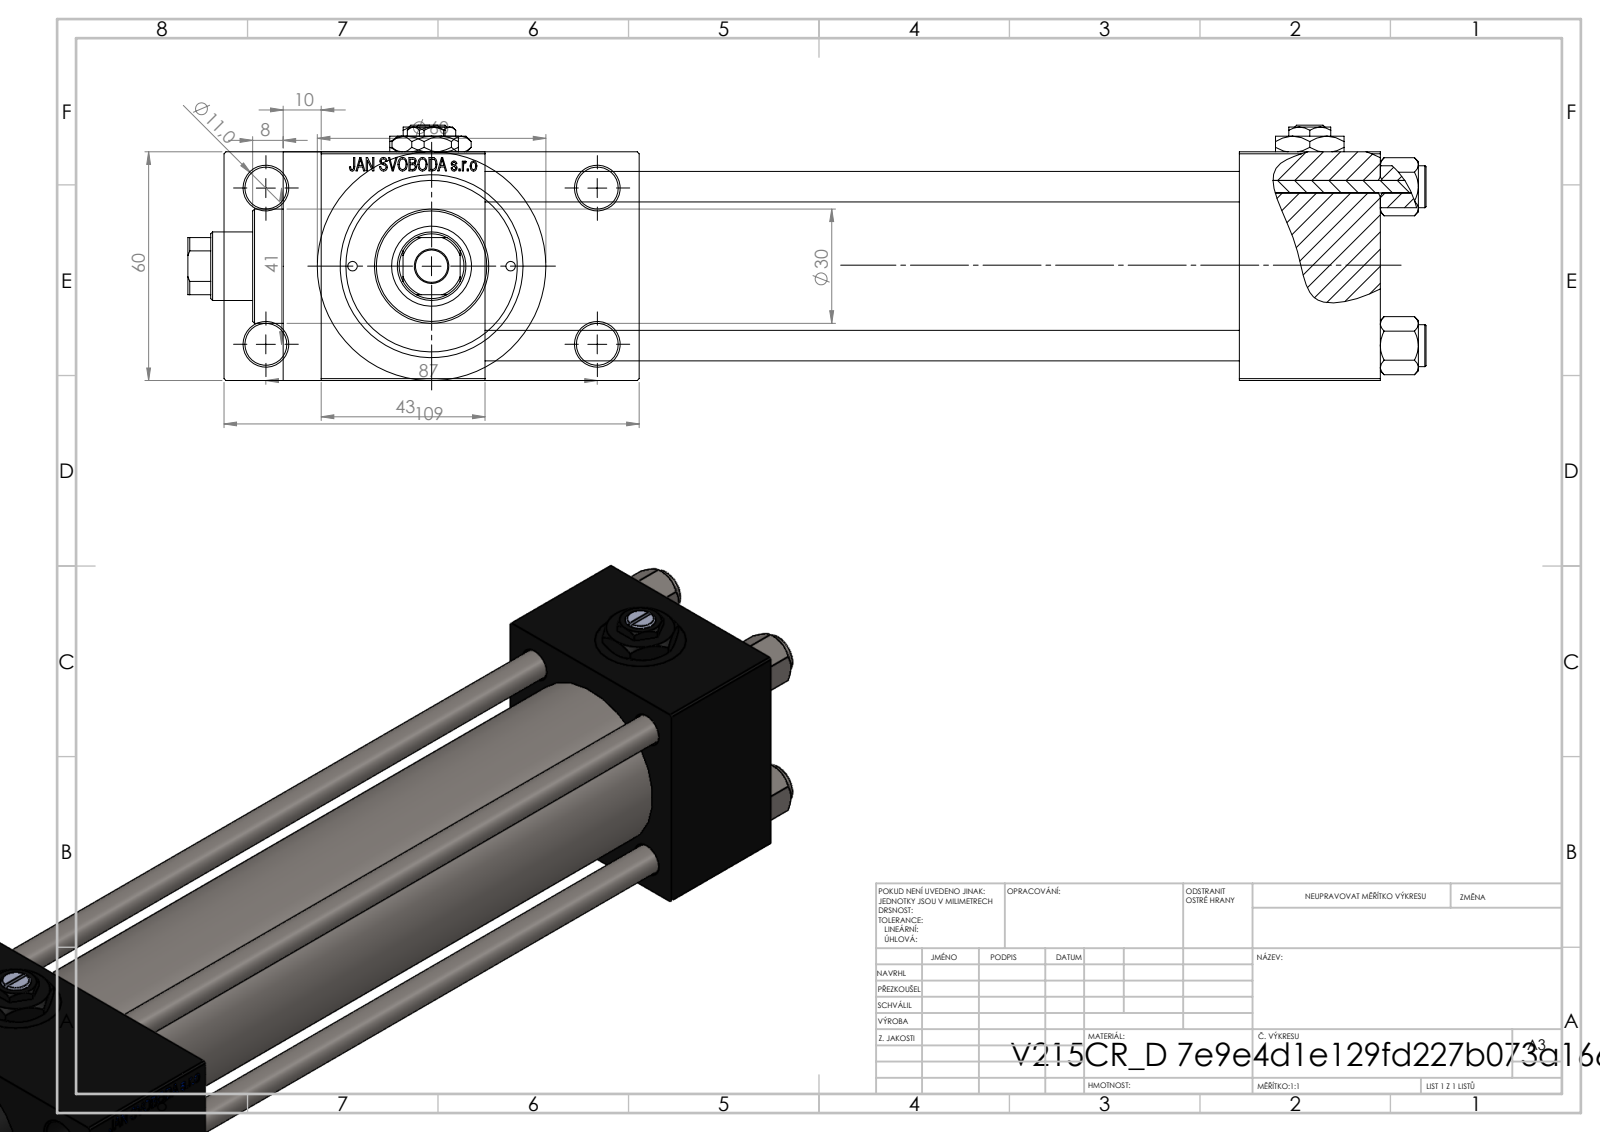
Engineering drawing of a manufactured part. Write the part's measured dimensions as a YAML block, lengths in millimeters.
part_name: "NUT_M5_D; V215CR_VCP_D; V215_VC_A; Zatka_pro_OIL_PORT (+2 more)"
step_written_by: "SolidWorks 2019 (CONFIG_CONTROL_DESIGN)"
units: millimeters
bodies: {solids: 13, faces: 1213, planar: 548, cylindrical: 103, other: 562}
overall_size: [325, 109, 67]
volume: 630637
surface_area: 184965
round_holes:
  - {diameter: 8, count: 4}
  - {diameter: 11, count: 4}
  - {diameter: 16.66, count: 4}
  - {diameter: 24, count: 4}
  - {diameter: 7, count: 3}
  - {diameter: 2.5, count: 2}
  - {diameter: 8.5, count: 1}
  - {diameter: 18, count: 1}
  - {diameter: 21, count: 1}
  - {diameter: 31, count: 1}
  - {diameter: 40, count: 1}
  - {diameter: 45, count: 1}
round_bosses_or_shafts:
  - {diameter: 11, count: 4}
  - {diameter: 60, count: 1}
  - {diameter: 46, count: 1}
  - {diameter: 30, count: 1}
partial_cylinders:
  - {radius: 8.5, count: 1}
face_to_face_distances: [60, 198, 24.5, 84.5, 37, 235, 43, 278, 241, 10]
hole_center_spacings: [20.85, 22.65, 29.49, 30.62, 41.7, 46.53, 47.15, 48.09]
